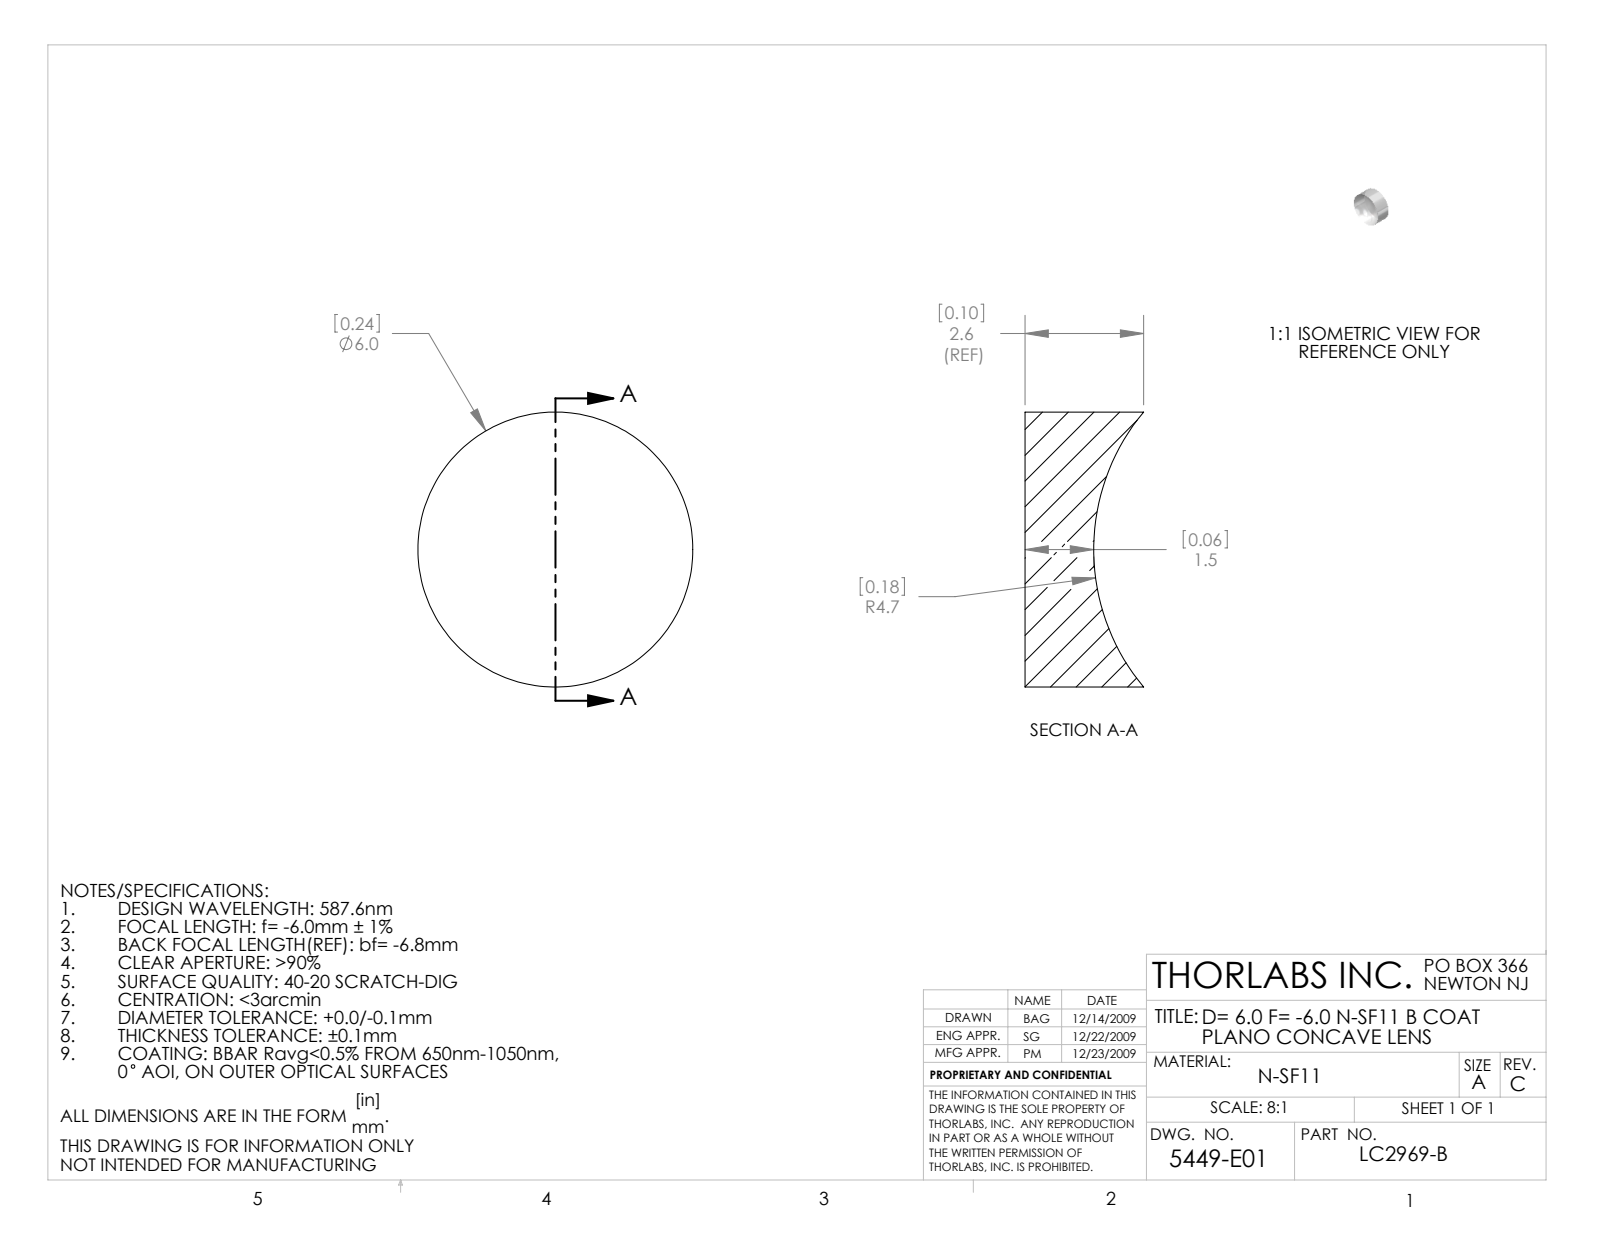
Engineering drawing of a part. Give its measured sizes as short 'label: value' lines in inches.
name: 5449-E0W
written by: SolidWorks 2009 (AUTOMOTIVE_DESIGN)
unit: in
bodies: 1 solid, 5 faces (1 planar, 2 cylindrical, 2 other)
size: 0.236 × 0.236 × 0.102
volume: 0.003 in³; area: 0.169 in²
bosses: 1× ⌀0.236
